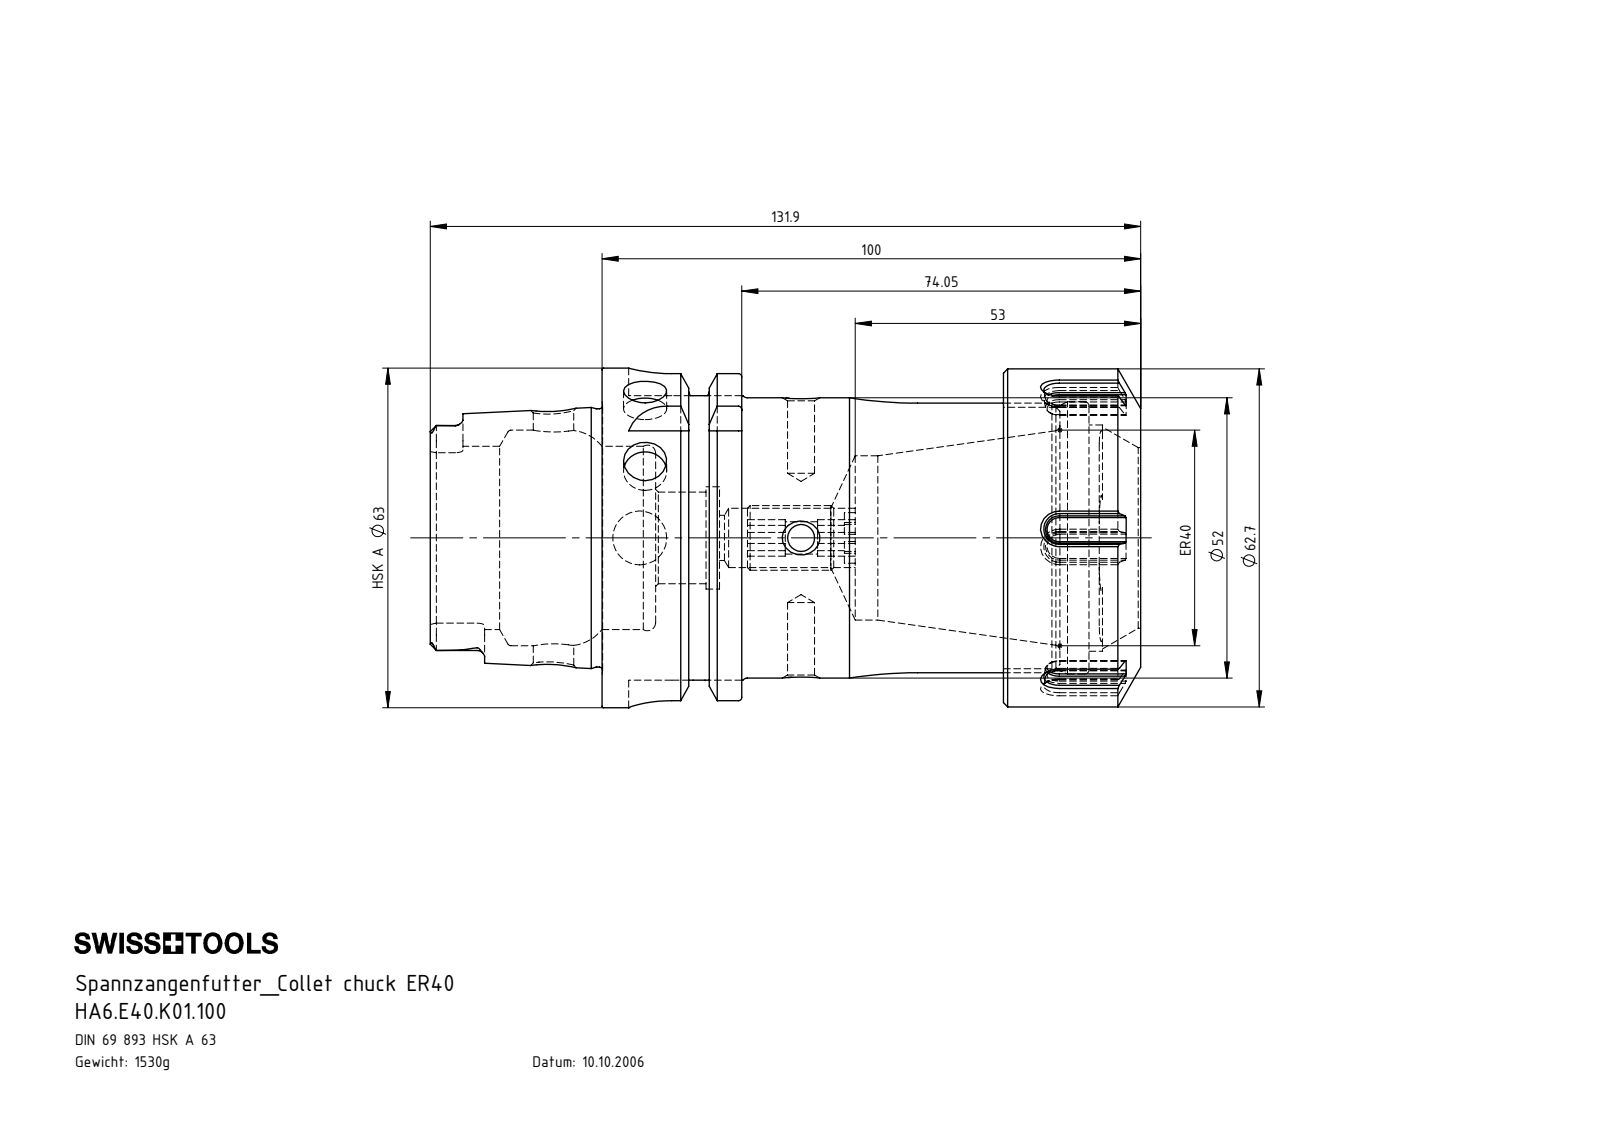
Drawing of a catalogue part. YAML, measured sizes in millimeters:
part_name: "HA6.E40.K01.100; ERU-AN5.K01.020_A; E40-ER1.001.025; HA6-E40.K01.100_B_Fertigbearbeitung"
step_written_by: "SolidWorks 2011 (CONFIG_CONTROL_DESIGN)"
units: millimeters
bodies: {solids: 3, faces: 334, planar: 133, cylindrical: 80, other: 121}
overall_size: [131.9, 63, 63]
volume: 194839
surface_area: 50406
round_holes:
  - {diameter: 5, count: 2}
  - {diameter: 8, count: 2}
  - {diameter: 6, count: 1}
  - {diameter: 7.5, count: 1}
  - {diameter: 8.4, count: 1}
  - {diameter: 10, count: 1}
  - {diameter: 11, count: 1}
  - {diameter: 17, count: 1}
  - {diameter: 19, count: 1}
  - {diameter: 30.5, count: 1}
  - {diameter: 33.5, count: 1}
  - {diameter: 34, count: 1}
round_bosses_or_shafts:
  - {diameter: 63, count: 1}
  - {diameter: 62.7, count: 1}
  - {diameter: 54.95, count: 1}
  - {diameter: 52, count: 1}
  - {diameter: 50, count: 1}
  - {diameter: 47.93, count: 1}
  - {diameter: 12, count: 1}
partial_cylinders:
  - {radius: 1.4, count: 6}
  - {radius: 2.88, count: 4}
  - {radius: 8, count: 4}
  - {radius: 19.26, count: 2}
face_to_face_distances: [74.5, 100, 25.5, 90.4, 15.9, 9.6, 25.95, 48.55, 64.45, 74.05]
hole_center_spacings: [29.95, 45.95]
